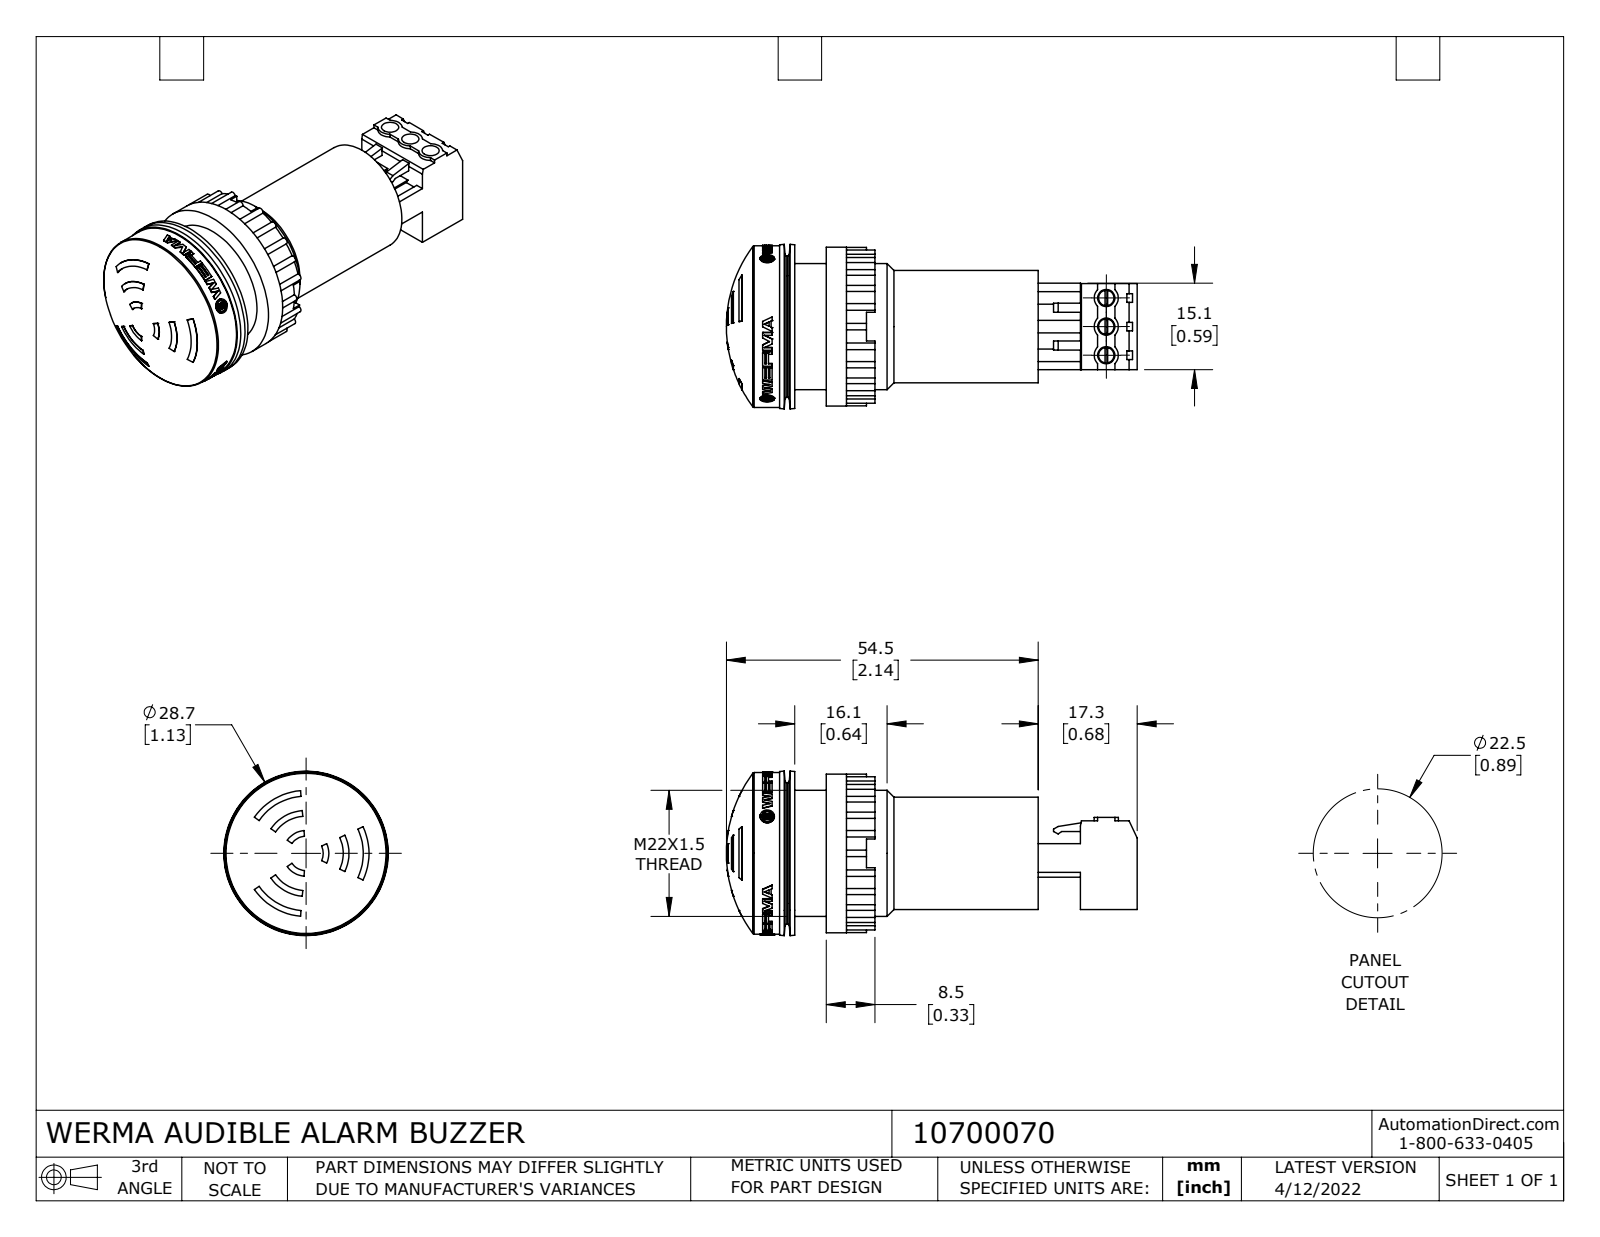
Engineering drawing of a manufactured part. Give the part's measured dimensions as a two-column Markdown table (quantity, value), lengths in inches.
| quantity | value |
| --- | --- |
| part name | 10700070 |
| STEP written by | SolidWorks 2021 (CONFIG_CONTROL_DESIGN) |
| units | inches |
| bodies | 1 solid, 617 faces (321 planar, 148 cylindrical, 148 other) |
| overall size | 2.82 × 1.13 × 1.13 |
| volume | 1.485 in³ |
| surface area | 11.49 in² |
| round holes (diameter × count) | 0.118 × 3 |
| round bosses / shafts (diameter × count) | 0.106 × 3, 1.11 × 1, 1.091 × 1, 0.972 × 1, 0.866 × 1, 0.772 × 1 |
| partial cylindrical surfaces (radius × count) | 0.023 × 24, 0.083 × 3, 0.112 × 3, 0.118 × 1, 0.157 × 1, 0.256 × 1, 0.295 × 1, 0.394 × 1 |
| main face-to-face distances | 1.457, 0.197, 0.591, 0.335, 0.291, 1.748, 1.413, 1.122, 0.39, 0.681 |
| hole center spacings | 0.197, 0.394 |
